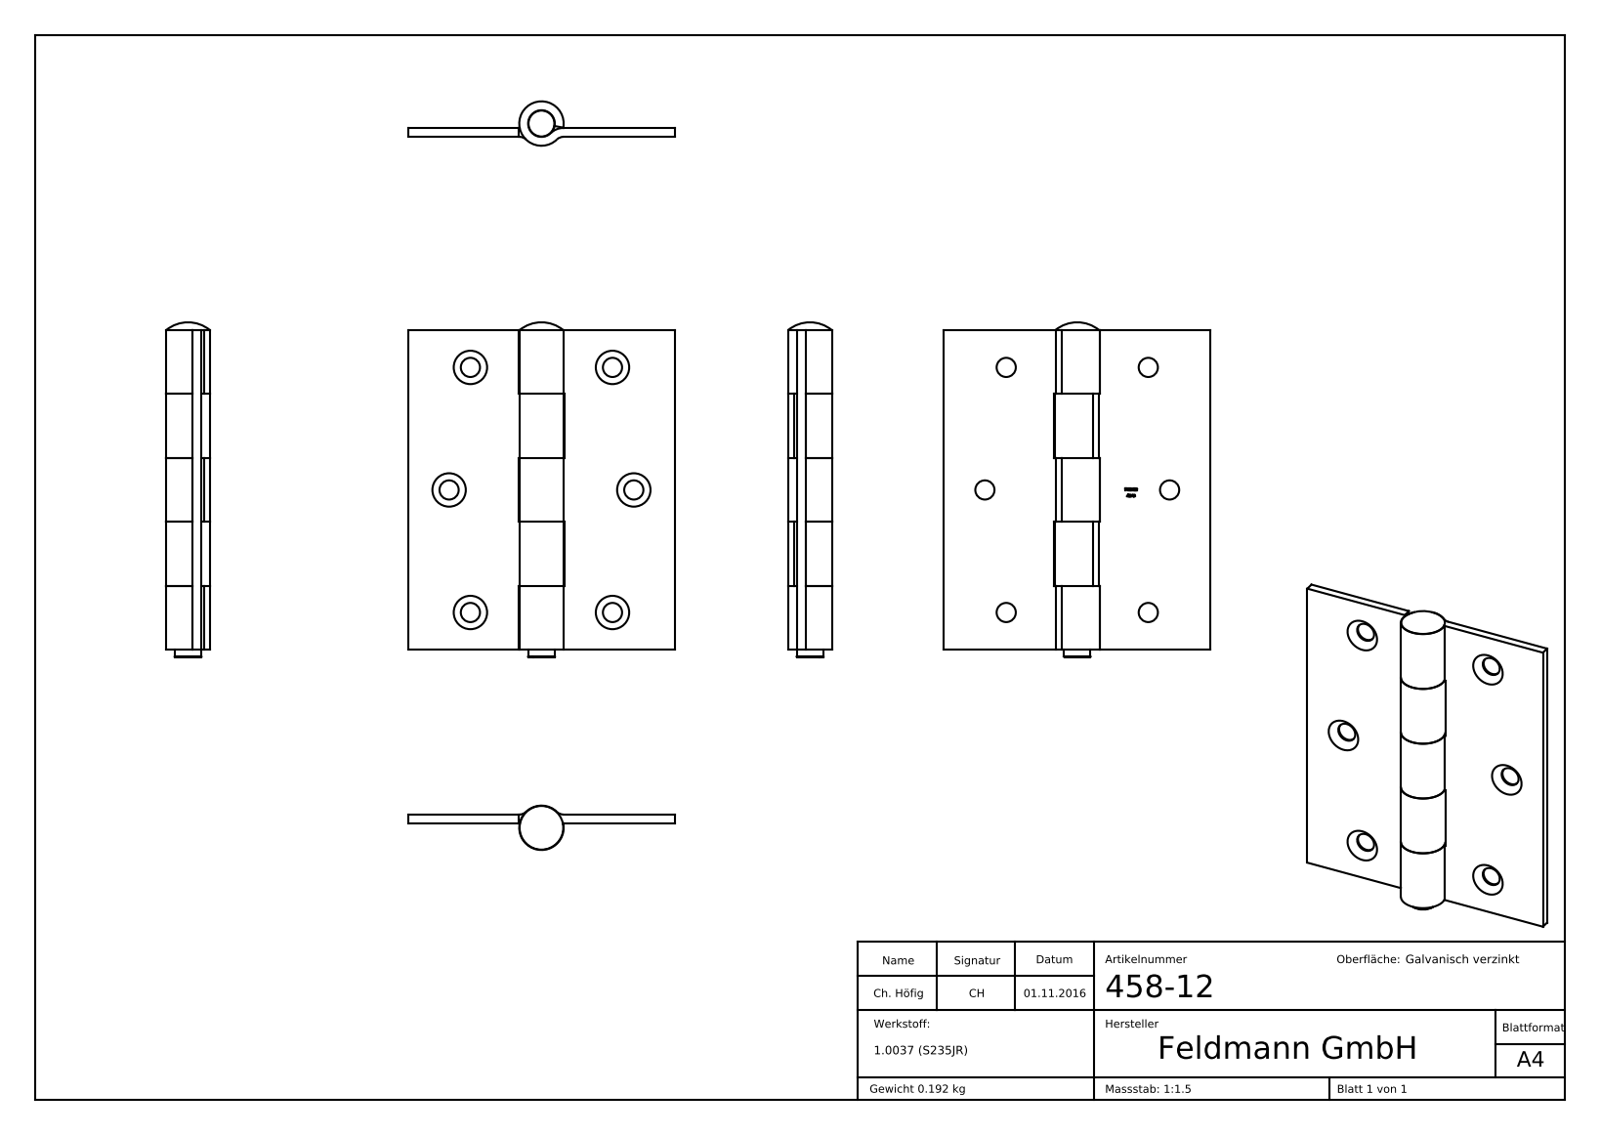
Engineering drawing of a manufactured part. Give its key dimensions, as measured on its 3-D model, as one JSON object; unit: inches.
{"part_name": "458-12 Teil2; 458-12 Teil3; 458-12; 458-12 Teil1", "step_written_by": "SolidWorks 2018 (CONFIG_CONTROL_DESIGN)", "units": "inches", "bodies": {"solids": 3, "faces": 253, "planar": 139, "cylindrical": 27, "other": 87}, "overall_size": [3.709, 2.953, 0.492], "volume_in3": 1.506, "surface_area_in2": 32.82, "round_holes": [[0.213, 6], [0.295, 1]], "round_bosses_or_shafts": [[0.492, 1]], "partial_cylinders_radius": [[0.098, 2], [0.197, 2]], "face_to_face_distances": [0.098, 0.709, 1.417, 2.126, 2.835, 3.543, 1.22, 1.732, 2.953, 0.512], "hole_center_spacings": [1.379, 2.264, 1.575, 2.717, 3.14, 2.047]}
